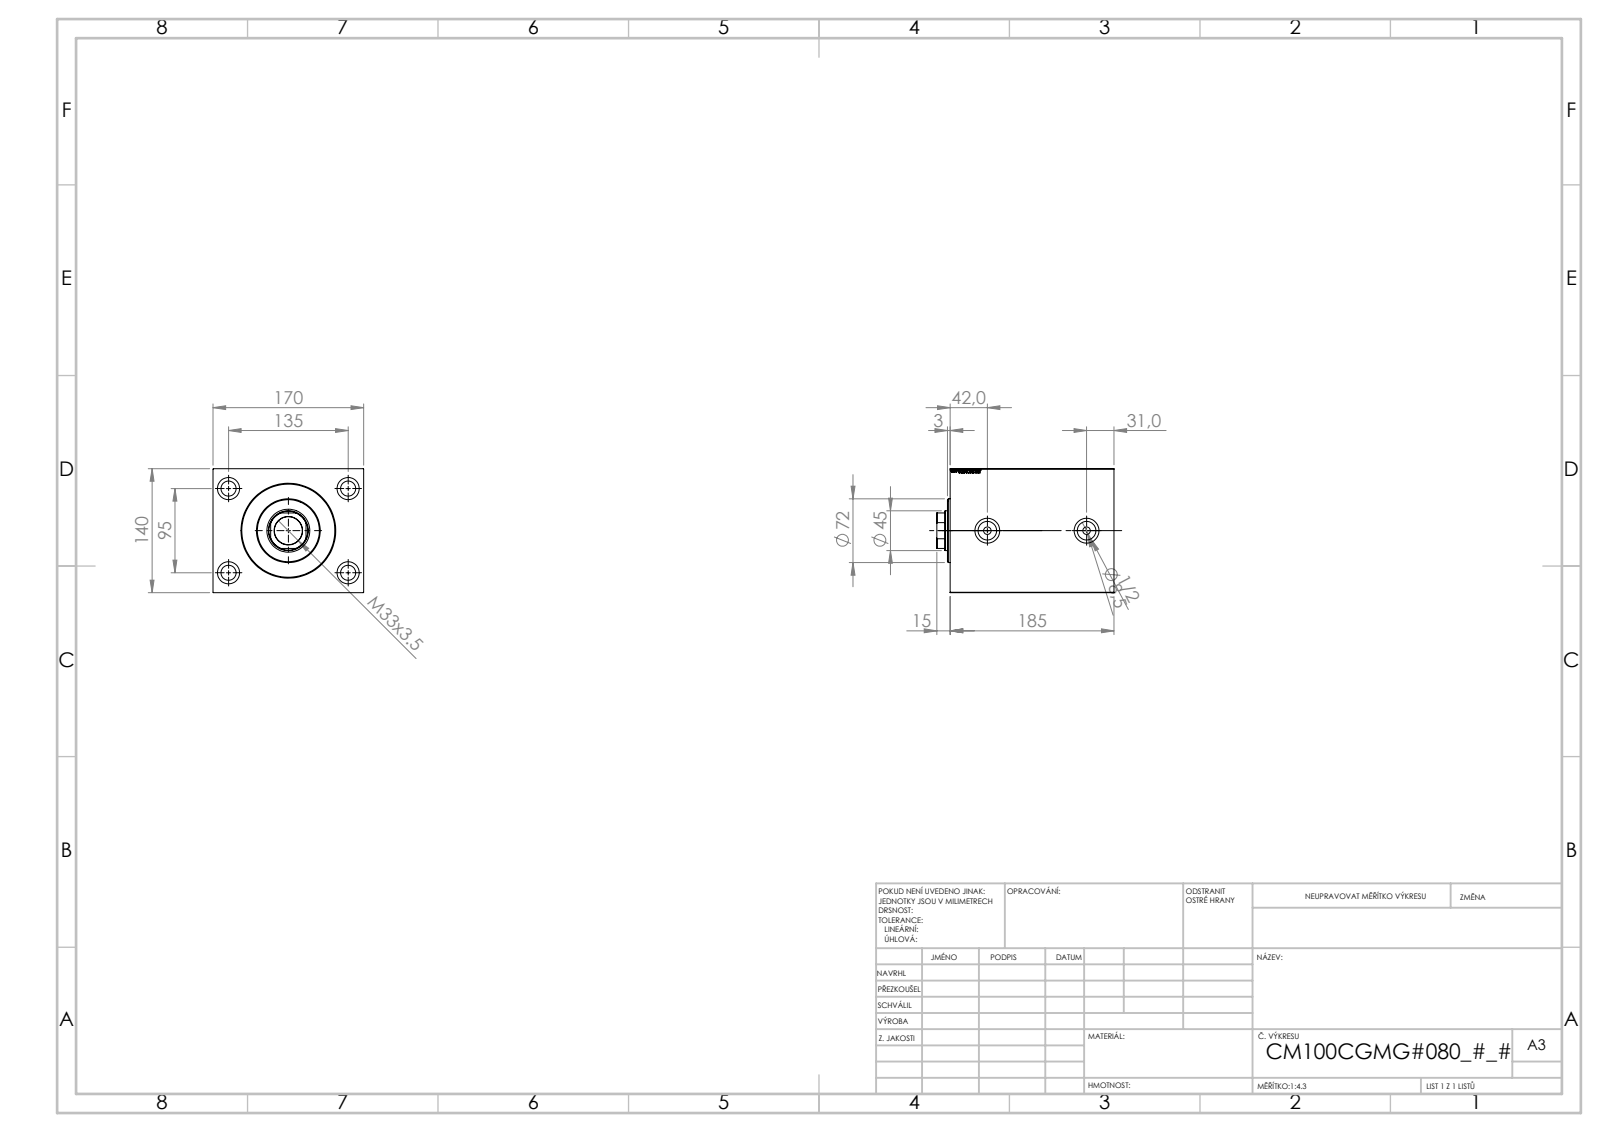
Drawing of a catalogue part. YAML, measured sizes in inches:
part_name: "V450CM_VC_B; V450CM_C_VCP; V450CM_C_Body"
step_written_by: "SolidWorks 2019 (CONFIG_CONTROL_DESIGN)"
units: inches
bodies: {solids: 3, faces: 865, planar: 409, cylindrical: 62, other: 394}
overall_size: [7.874, 6.693, 5.512]
volume: 224.8
surface_area: 516.4
round_holes:
  - {diameter: 0.669, count: 4}
  - {diameter: 0.984, count: 4}
  - {diameter: 0.335, count: 2}
  - {diameter: 0.825, count: 2}
  - {diameter: 1.102, count: 2}
  - {diameter: 1.24, count: 1}
  - {diameter: 1.772, count: 1}
  - {diameter: 1.909, count: 1}
  - {diameter: 3.937, count: 1}
  - {diameter: 4.016, count: 1}
  - {diameter: 4.134, count: 1}
round_bosses_or_shafts:
  - {diameter: 2.835, count: 1}
partial_cylinders:
  - {radius: 0.866, count: 1}
face_to_face_distances: [6.693, 5.512, 7.283, 6.26, 1.024, 3.543, 0.591, 5.669, 3.74, 3.15]
hole_center_spacings: [3.25, 3.74, 5.315, 6.499, 4.409]
